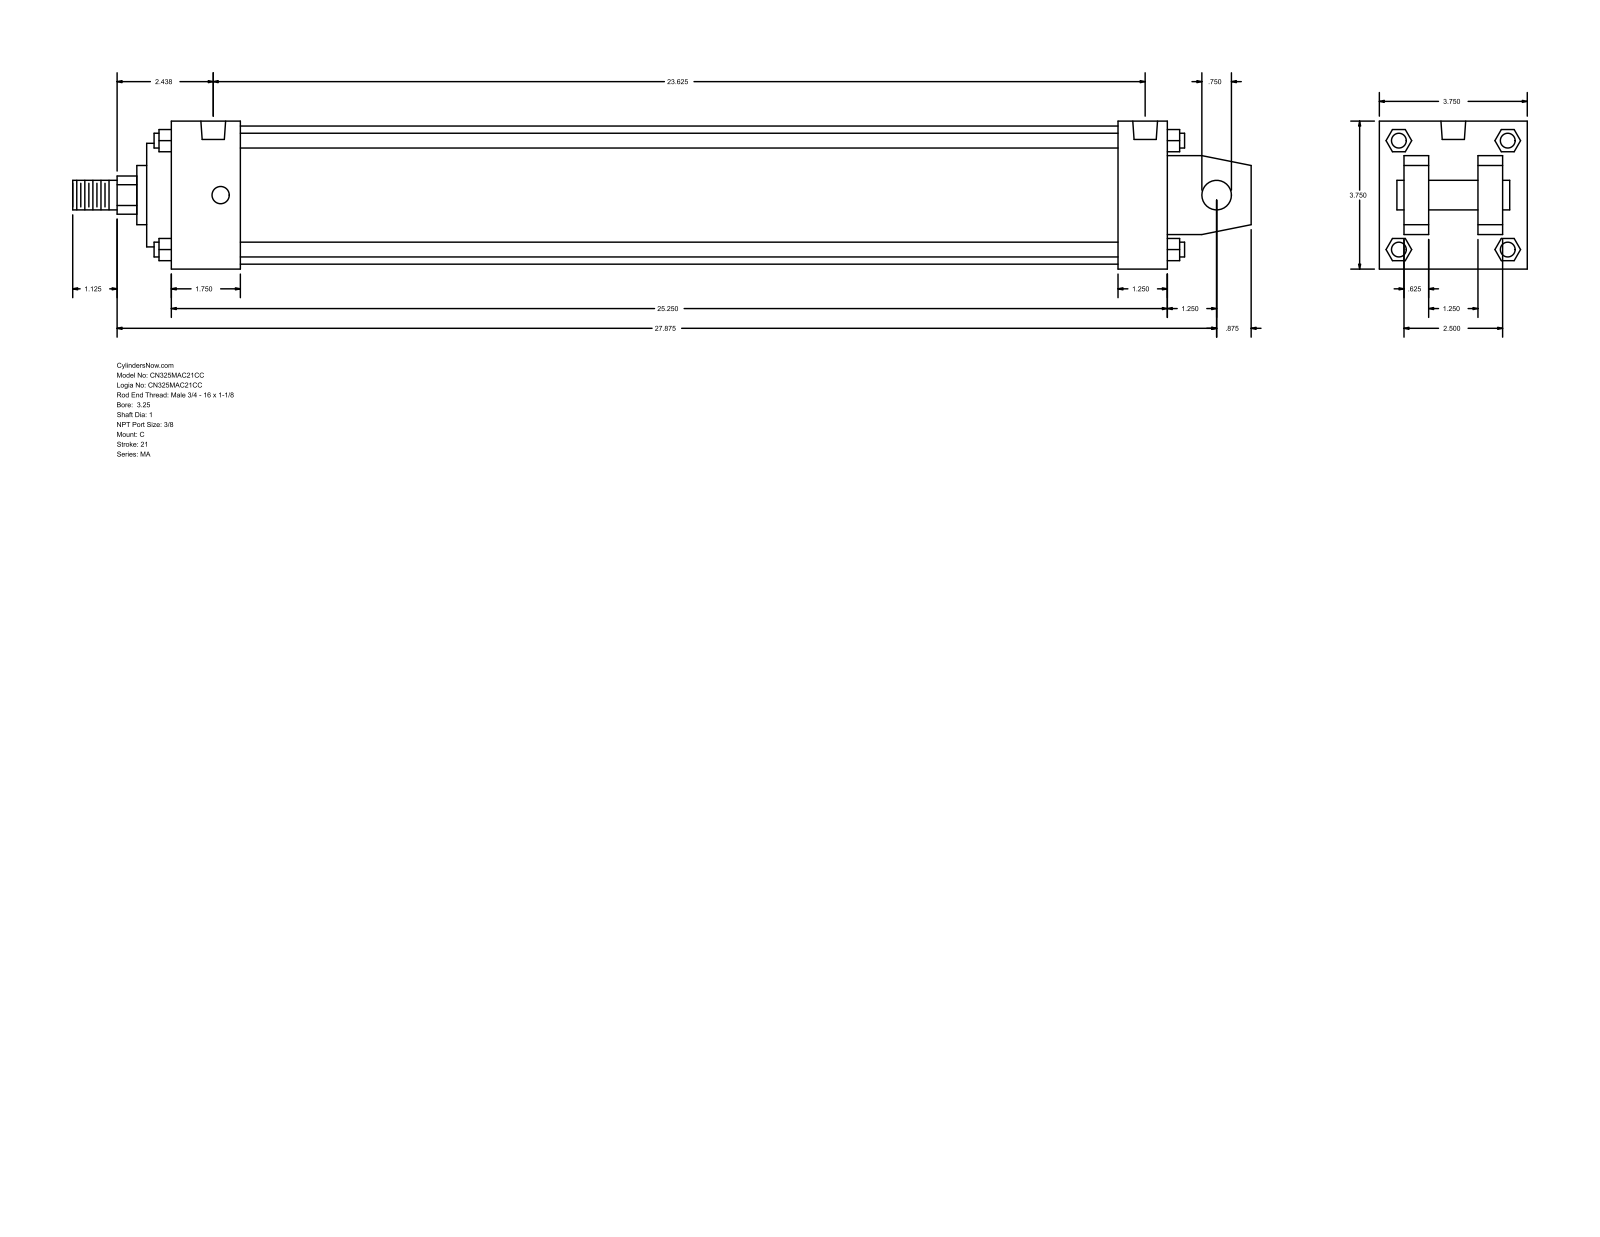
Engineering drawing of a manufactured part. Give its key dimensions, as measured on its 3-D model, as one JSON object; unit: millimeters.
{"part_name": "MA_C__0325_1", "step_written_by": "GSSL Pune (CONFIG_CONTROL_DESIGN)", "units": "millimeters", "bodies": {"solids": 0, "faces": 141, "planar": 109, "cylindrical": 32, "other": 0}, "overall_size": [758.83, 95.25, 95.25], "round_holes": [[11.11, 4], [15.93, 2]], "round_bosses_or_shafts": [[9.53, 4], [19.05, 2], [88.9, 1], [66.67, 1], [38.1, 1], [25.4, 1]], "partial_cylinders_radius": [[12.29, 1]], "face_to_face_distances": [95.24, 15.87, 63.5, 641.35, 31.74, 79.37, 47.63, 657.22, 609.6, 31.75], "hole_center_spacings": [4.76, 590.56, 595.32, 600.08]}
